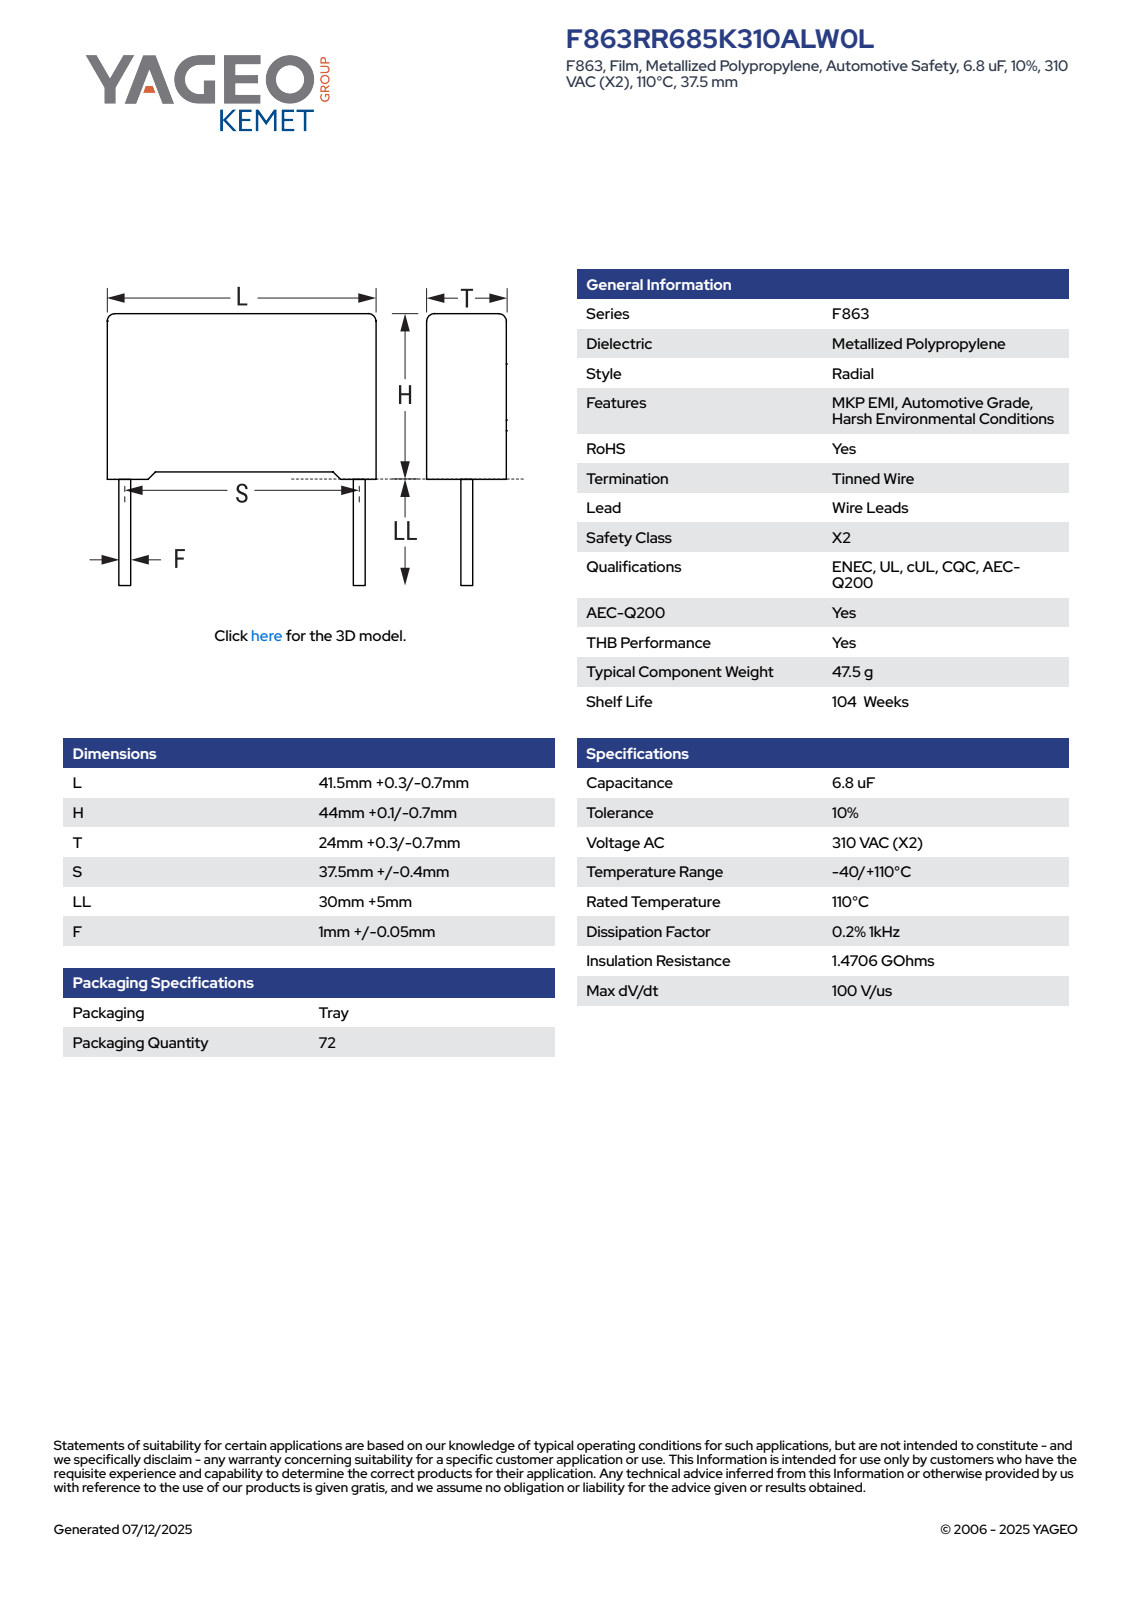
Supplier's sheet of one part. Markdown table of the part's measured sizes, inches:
| quantity | value |
| --- | --- |
| part name | CFR_RB2_41.5X44X24_L41.8H44.1T24.3S37.5LL35F1.05 |
| STEP written by | SolidWorks 2021 (AUTOMOTIVE_DESIGN) |
| units | inches |
| bodies | 4 solids, 85 faces (77 planar, 8 cylindrical, 0 other) |
| overall size | 3.114 × 1.646 × 0.957 |
| volume | 2.657 in³ |
| surface area | 12.65 in² |
| round bosses / shafts (diameter × count) | 0.041 × 2 |
| partial cylindrical surfaces (radius × count) | 0.02 × 4 |
| main face-to-face distances | 0.957, 1.646, 1.676, 0.03, 1.707, 0.03, 0.06, 1.736, 0.055, 1.591 |
